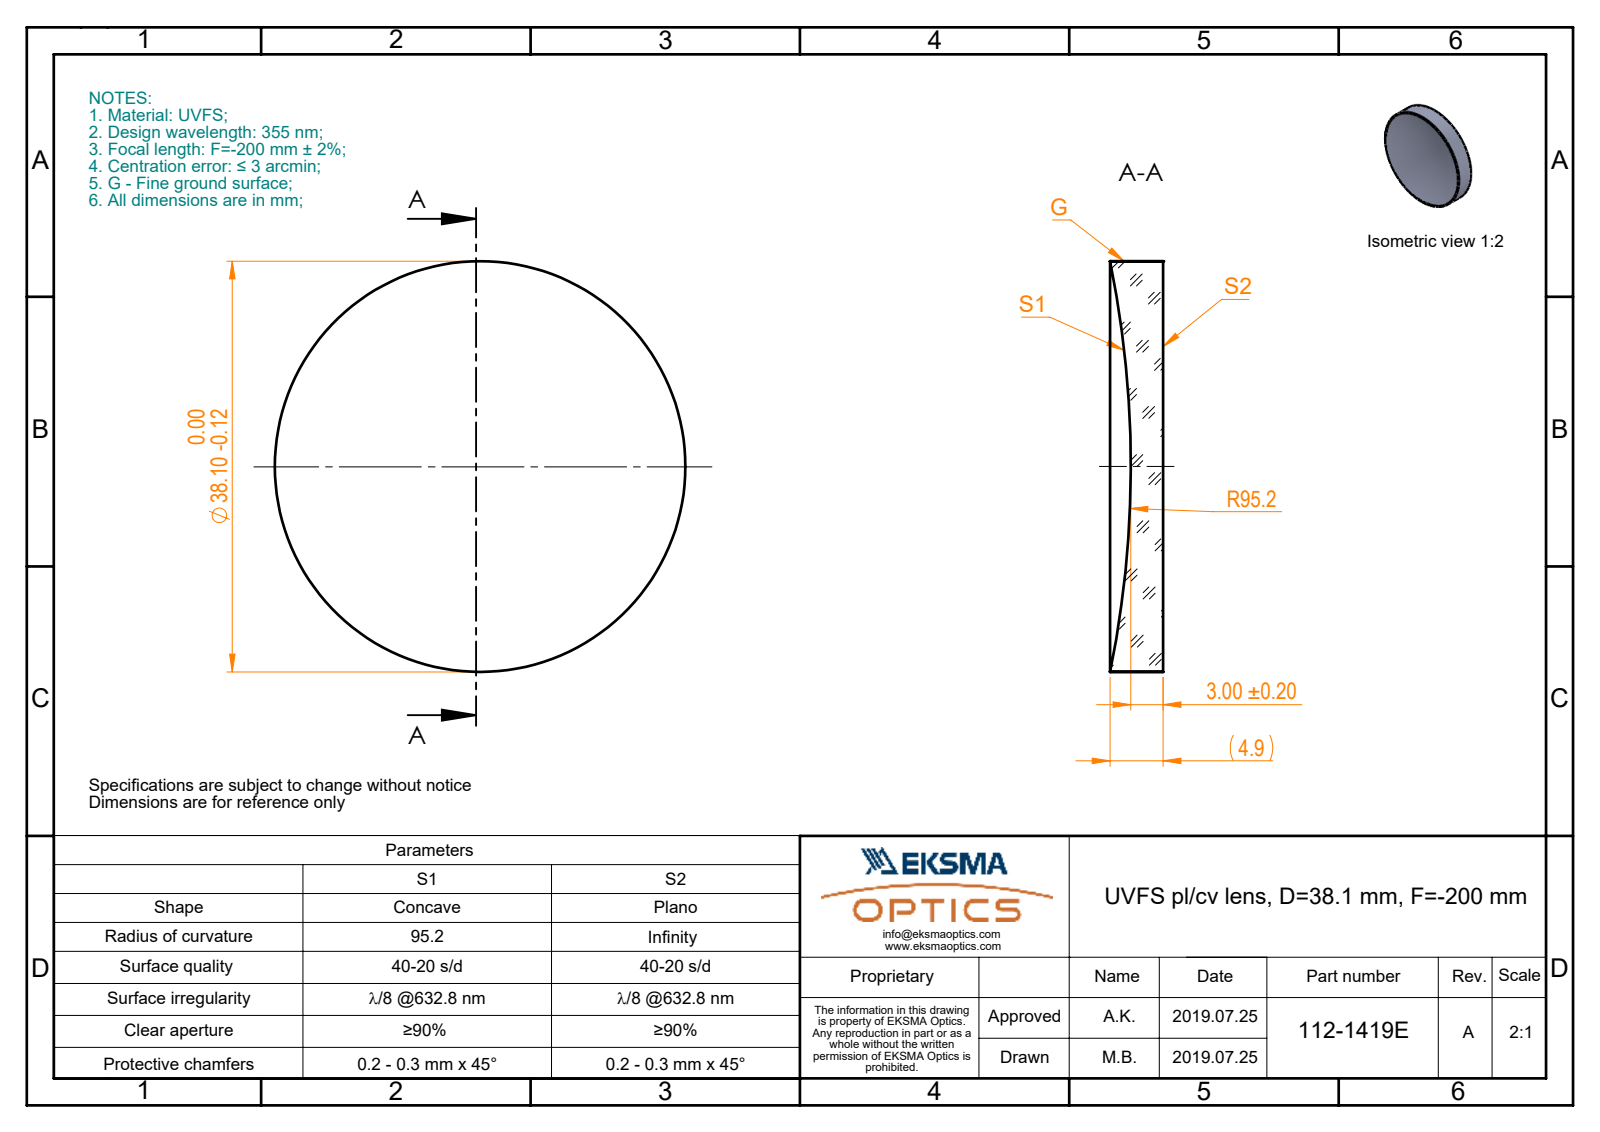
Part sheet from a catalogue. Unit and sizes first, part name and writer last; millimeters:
Units: millimetres
Overall size (bounding box): 38.1 × 38.1 × 4.92
Round bosses / shafts (diameter × count): ⌀38.1 ×1
Volume: 4 514 mm³ · Surface area: 2 881 mm²
Bodies: 1 solid, 5 faces (1 planar, 2 cylindrical, 2 other)
Part name (STEP PRODUCT): 112-1419E UVFS pl-cv 38.1 F-200
STEP written by: SolidWorks 2017 (CONFIG_CONTROL_DESIGN)
